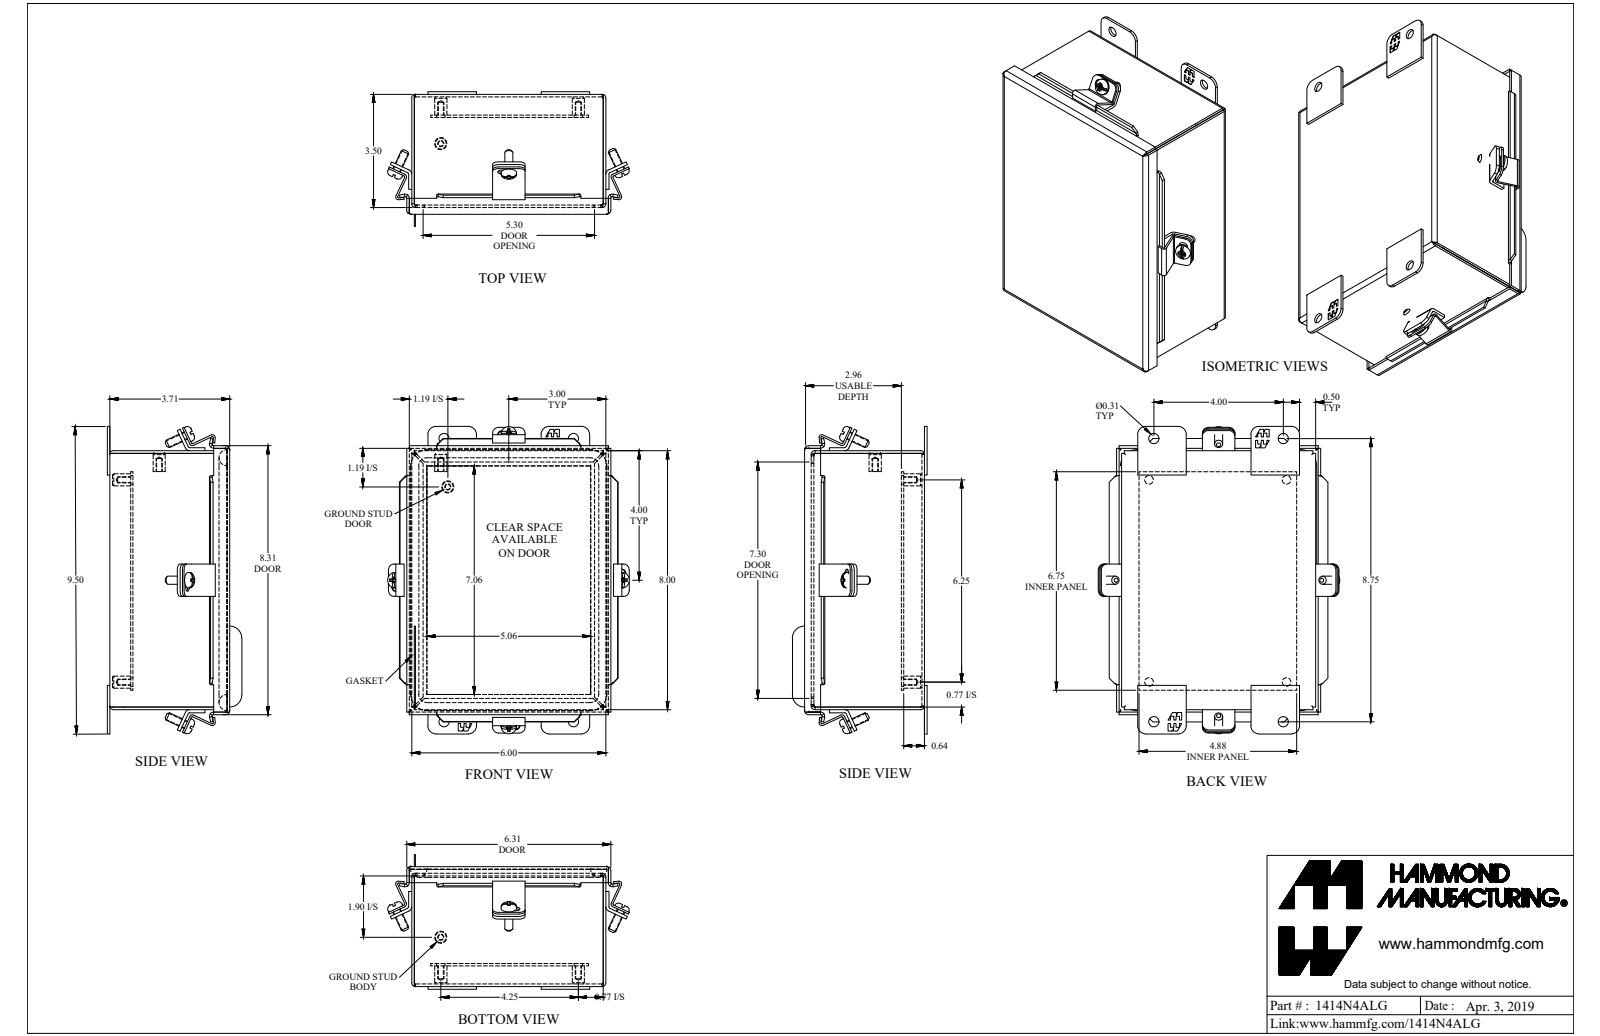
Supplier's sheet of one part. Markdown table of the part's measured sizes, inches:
| quantity | value |
| --- | --- |
| part name | 1414N4ALG |
| STEP written by | SolidWorks 2018 (AUTOMOTIVE_DESIGN) |
| units | inches |
| bodies | 26 solids, 727 faces (499 planar, 162 cylindrical, 66 other) |
| overall size | 9.5 × 7.471 × 3.786 |
| volume | 24.29 in³ |
| surface area | 618.8 in² |
| round holes (diameter × count) | 0.159 × 6, 0.213 × 4, 0.265 × 4, 0.313 × 4 |
| round bosses / shafts (diameter × count) | 0.375 × 6, 0.33 × 6, 0.48 × 4, 0.25 × 4 |
| partial cylindrical surfaces (radius × count) | 0.25 × 12, 0.01 × 8, 0.029 × 8, 0.036 × 8, 0.048 × 8, 0.086 × 8, 0.117 × 8, 0.141 × 8 |
| main face-to-face distances | 0.081, 3.625, 5.919, 3.706, 3.544, 7.919, 0.562, 0.643, 3.063, 2.982 |
| hole center spacings | 4, 4.25, 6.25, 7.558, 0.31, 1.23, 1.235, 1.278 |
